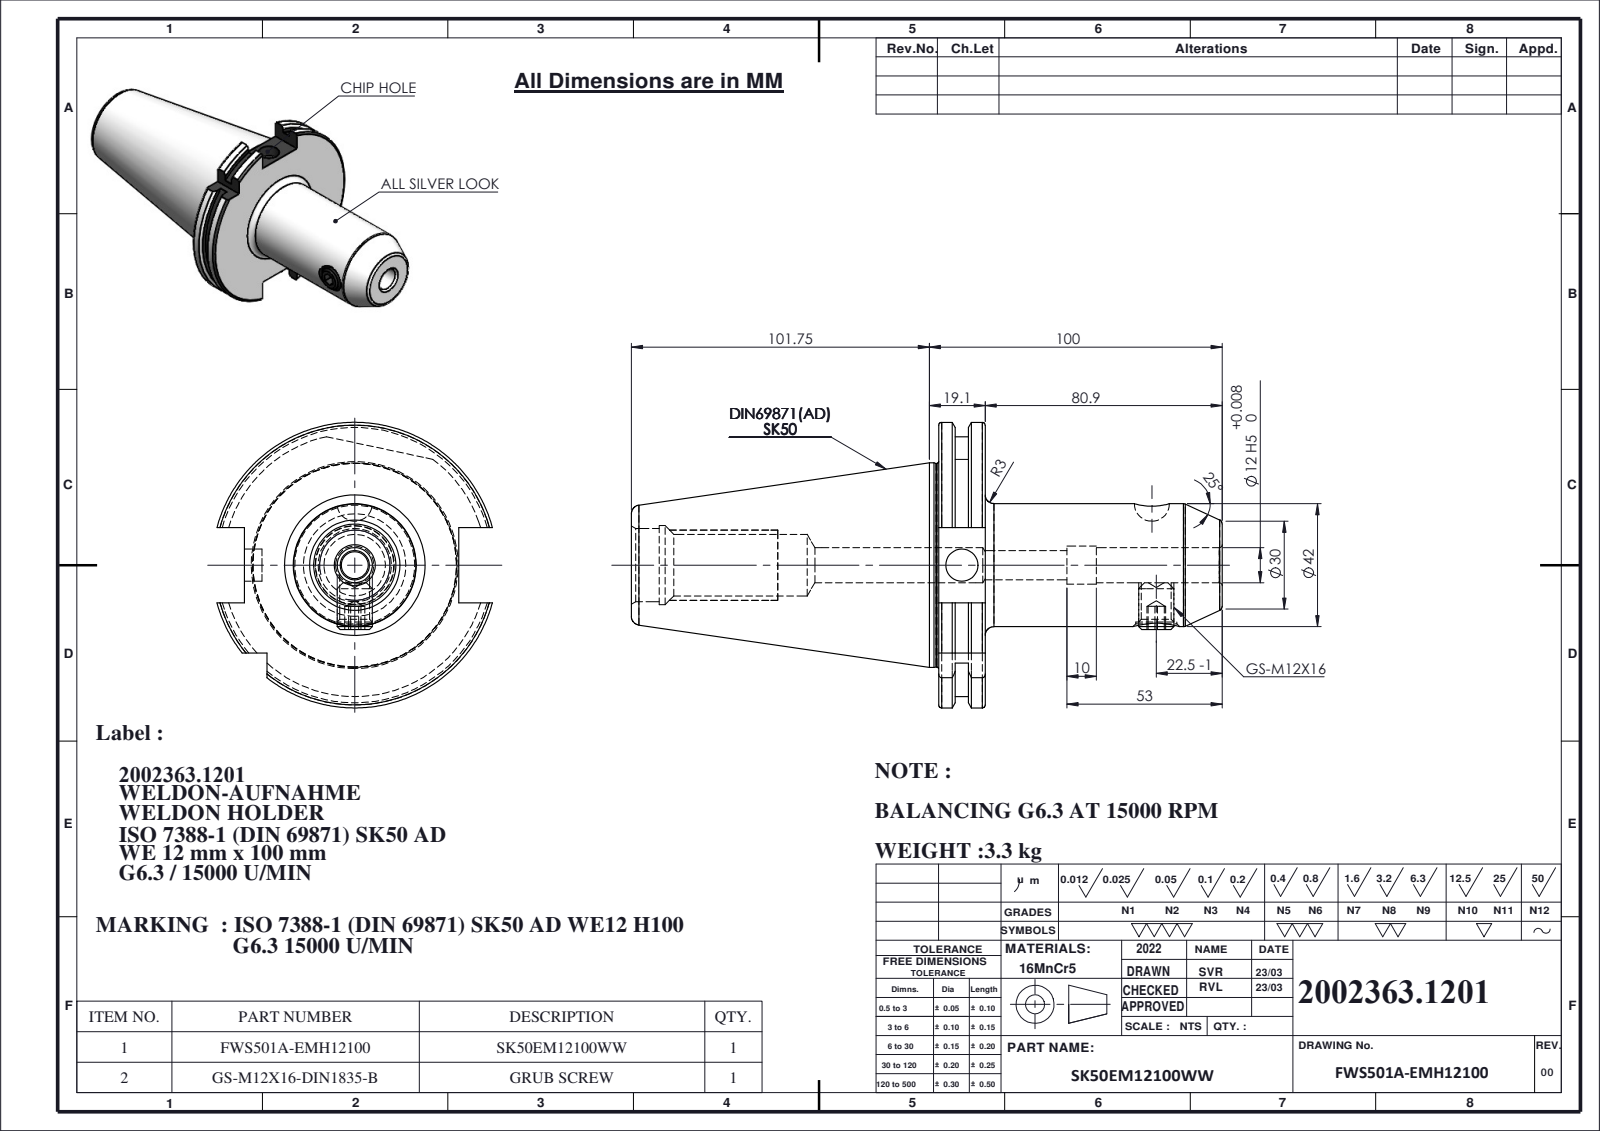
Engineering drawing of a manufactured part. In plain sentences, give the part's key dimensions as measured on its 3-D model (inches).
The part is named "SK50EM12100WW; GS-M12X16-DIN1835-B; 91506-WE112100". Its 3-D file was written by "SolidWorks 2018 (CONFIG_CONTROL_DESIGN)". It is 2 solids with 139 faces: 39 planar, 41 cylindrical and 59 other. Overall it measures 7.943 by 3.839 by 3.703 inches. Its volume is 26.34 cubic inches and its surface area 87.83 square inches. Round holes: 1 of diameter 0.394, 1 of diameter 0.402, 1 of diameter 0.433, 1 of diameter 0.472, 1 of diameter 0.512, 1 of diameter 0.551, 1 of diameter 0.827, 1 of diameter 0.984, 1 of diameter 1.063. Round bosses or shafts: 1 of diameter 2.75, 1 of diameter 2.734, 1 of diameter 1.654, 1 of diameter 0.472. Partial cylindrical surfaces (rounded edges, fillets, slot ends): 1 of radius 1.768, 1 of radius 1.919. The main face-to-face distances are 0.626, 0.223, 0.403, 0.4, 0.177, 0.226, 3.811, 3.588, 3.411, 3.185.
